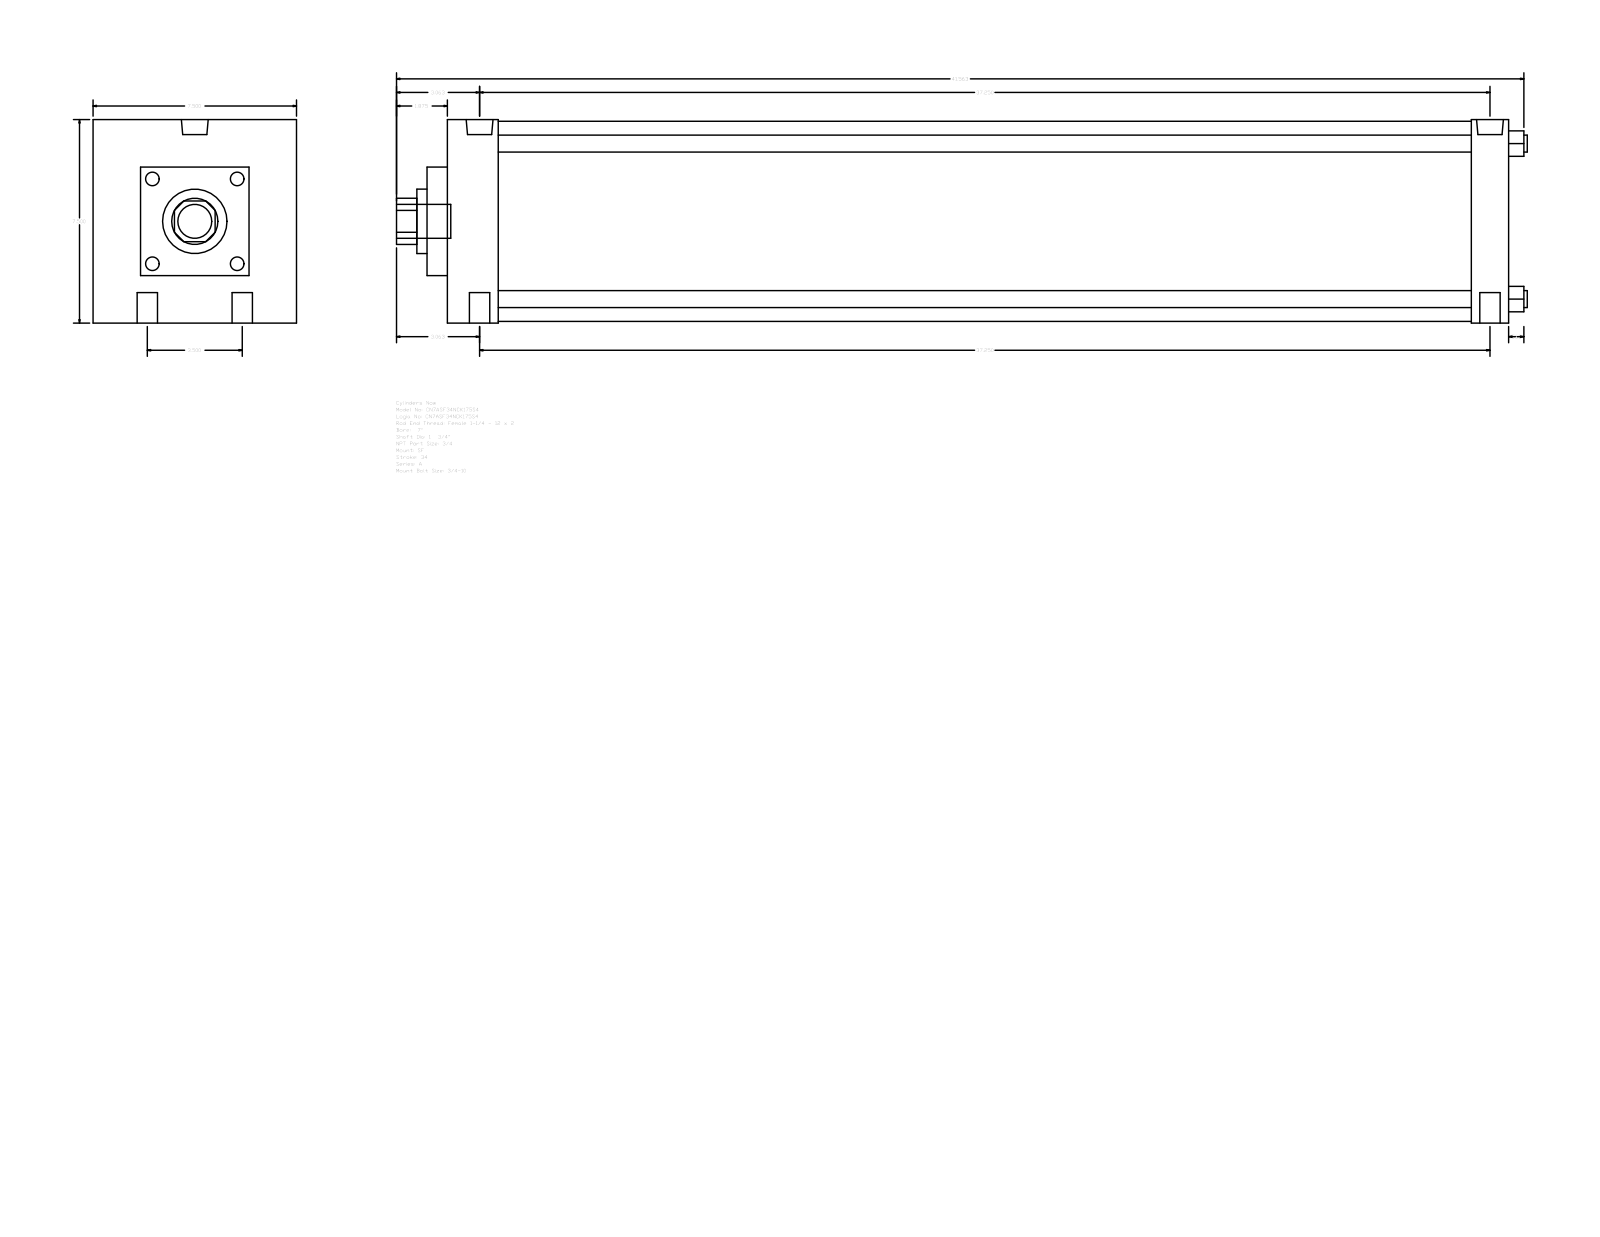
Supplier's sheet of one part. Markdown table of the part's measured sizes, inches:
| quantity | value |
| --- | --- |
| part name | A_SF__0700_1.75 |
| STEP written by | GSSL Pune (CONFIG_CONTROL_DESIGN) |
| units | inches |
| bodies | 0 solids, 93 faces (67 planar, 26 cylindrical, 0 other) |
| overall size | 41.687 × 7.5 × 7.5 |
| round holes (diameter × count) | 0.75 × 4, 0.594 × 2, 0.989 × 2, 1.75 × 1, 2.375 × 1 |
| round bosses / shafts (diameter × count) | 0.625 × 4, 7.375 × 1, 1.25 × 1 |
| partial cylindrical surfaces (radius × count) | 0.852 × 1 |
| main face-to-face distances | 7.5, 39.125, 1.75, 1.375, 0.75, 1.875, 37.75, 35.875, 37.25, 5.75 |
| hole center spacings | 1.75, 37.291, 37.25, 3.5, 37.414, 36.812 |
